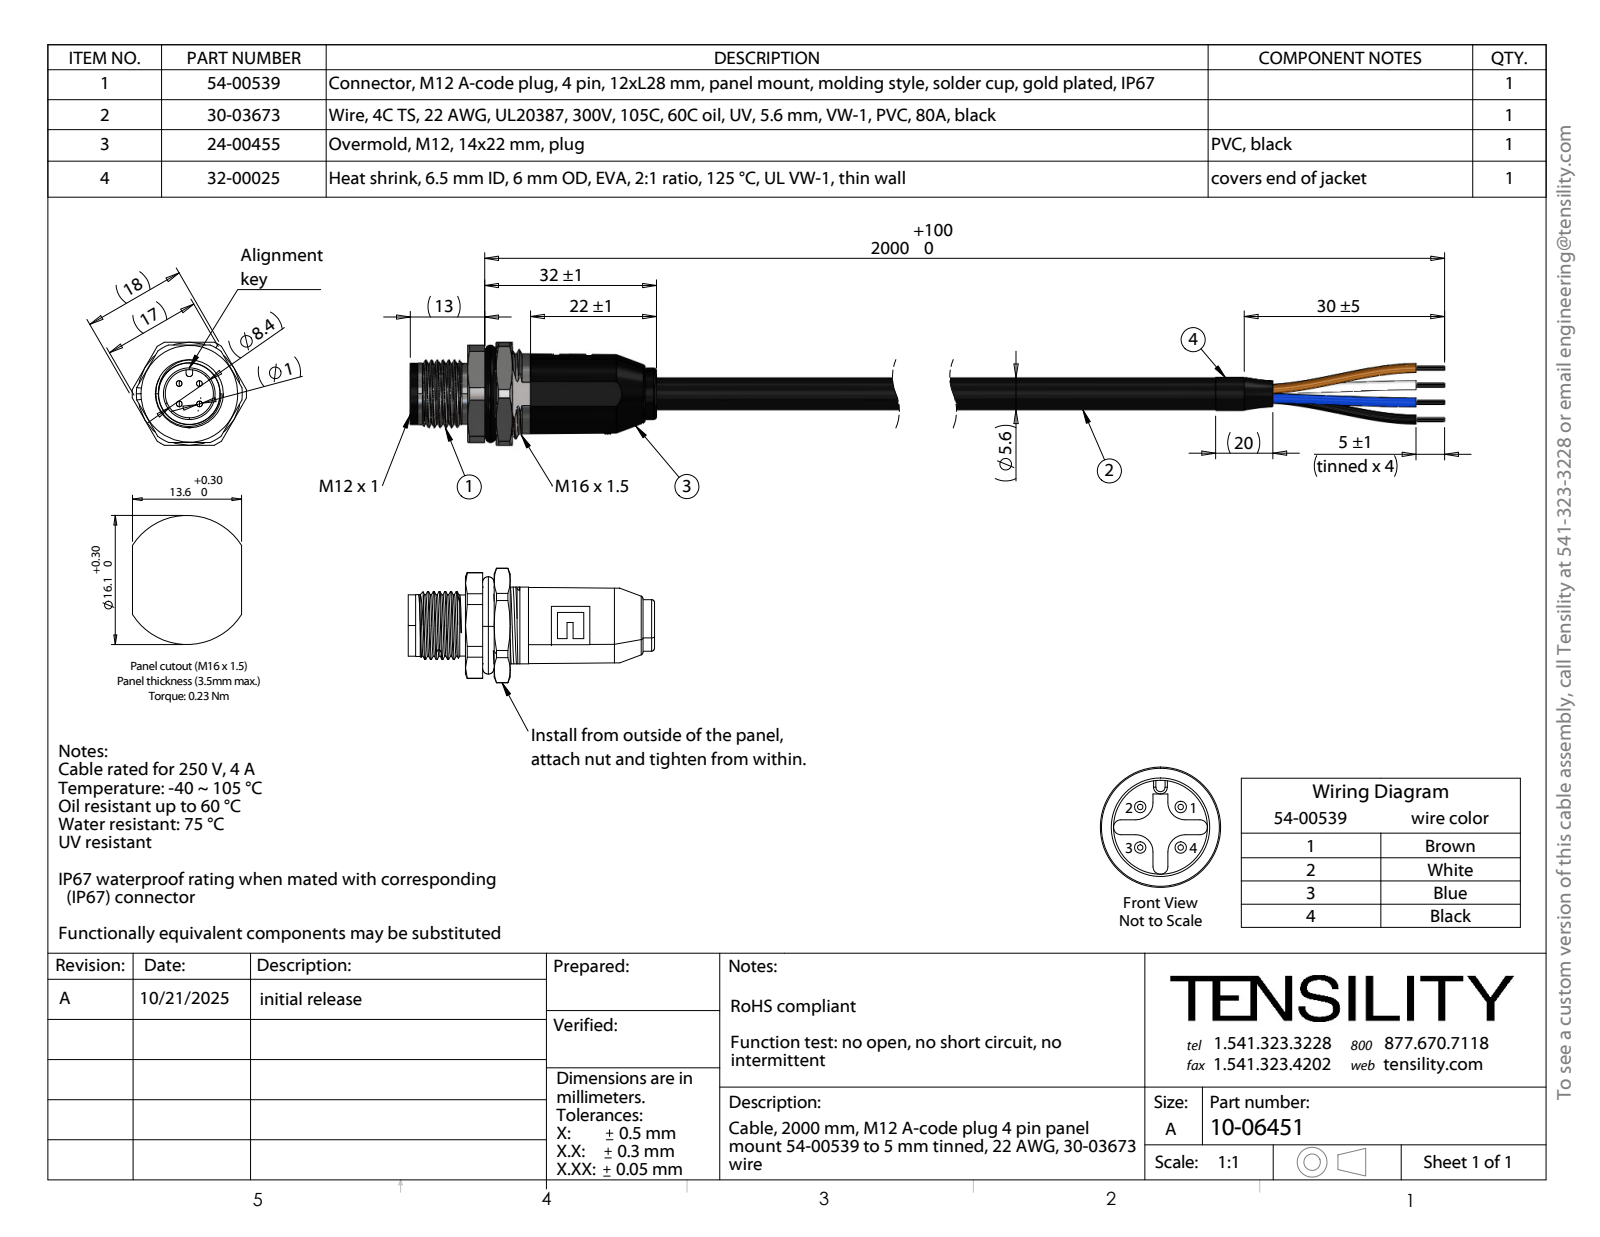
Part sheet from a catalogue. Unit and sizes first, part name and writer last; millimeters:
Units: millimetres
Overall size (bounding box): 227.99 × 20 × 18
Round holes (diameter × count): ⌀1.6 ×4, ⌀1 ×3, ⌀0.96 ×1, ⌀3.88 ×1, ⌀4.28 ×1, ⌀6.5 ×1, ⌀8.4 ×1, ⌀9.4 ×1, ⌀9.6 ×1, ⌀12.2 ×1, ⌀14.7 ×1
Round bosses / shafts (diameter × count): ⌀1.5 ×4, ⌀1.4 ×4, ⌀13.94 ×1, ⌀12.5 ×1, ⌀11.86 ×1, ⌀11 ×1, ⌀10.8 ×1, ⌀10.7 ×1
Partial cylindrical surfaces — rounded edges, fillets, slot ends (radius × count): R0.5 ×2, R7.04 ×1, R7.9 ×1, R9.25 ×1, R10 ×1
Main face-to-face distances: 8, 11, 2, 0.5, 1.5, 3, 17.5, 18, 10, 2.8
Hole centre spacings: 0.48, 0.37, 1.62, 0.31, 0.33, 1.78, 0.32, 1.45
Volume: 9 543 mm³ · Surface area: 34 133 mm²
Bodies: 150 solids, 1215 faces (474 planar, 576 cylindrical, 165 other)
Part name (STEP PRODUCT): 54-00539; 24-00455; 32-00025_10 mm; 30-03673_spec (+2 more)
STEP written by: SolidWorks 2025 (CONFIG_CONTROL_DESIGN)
